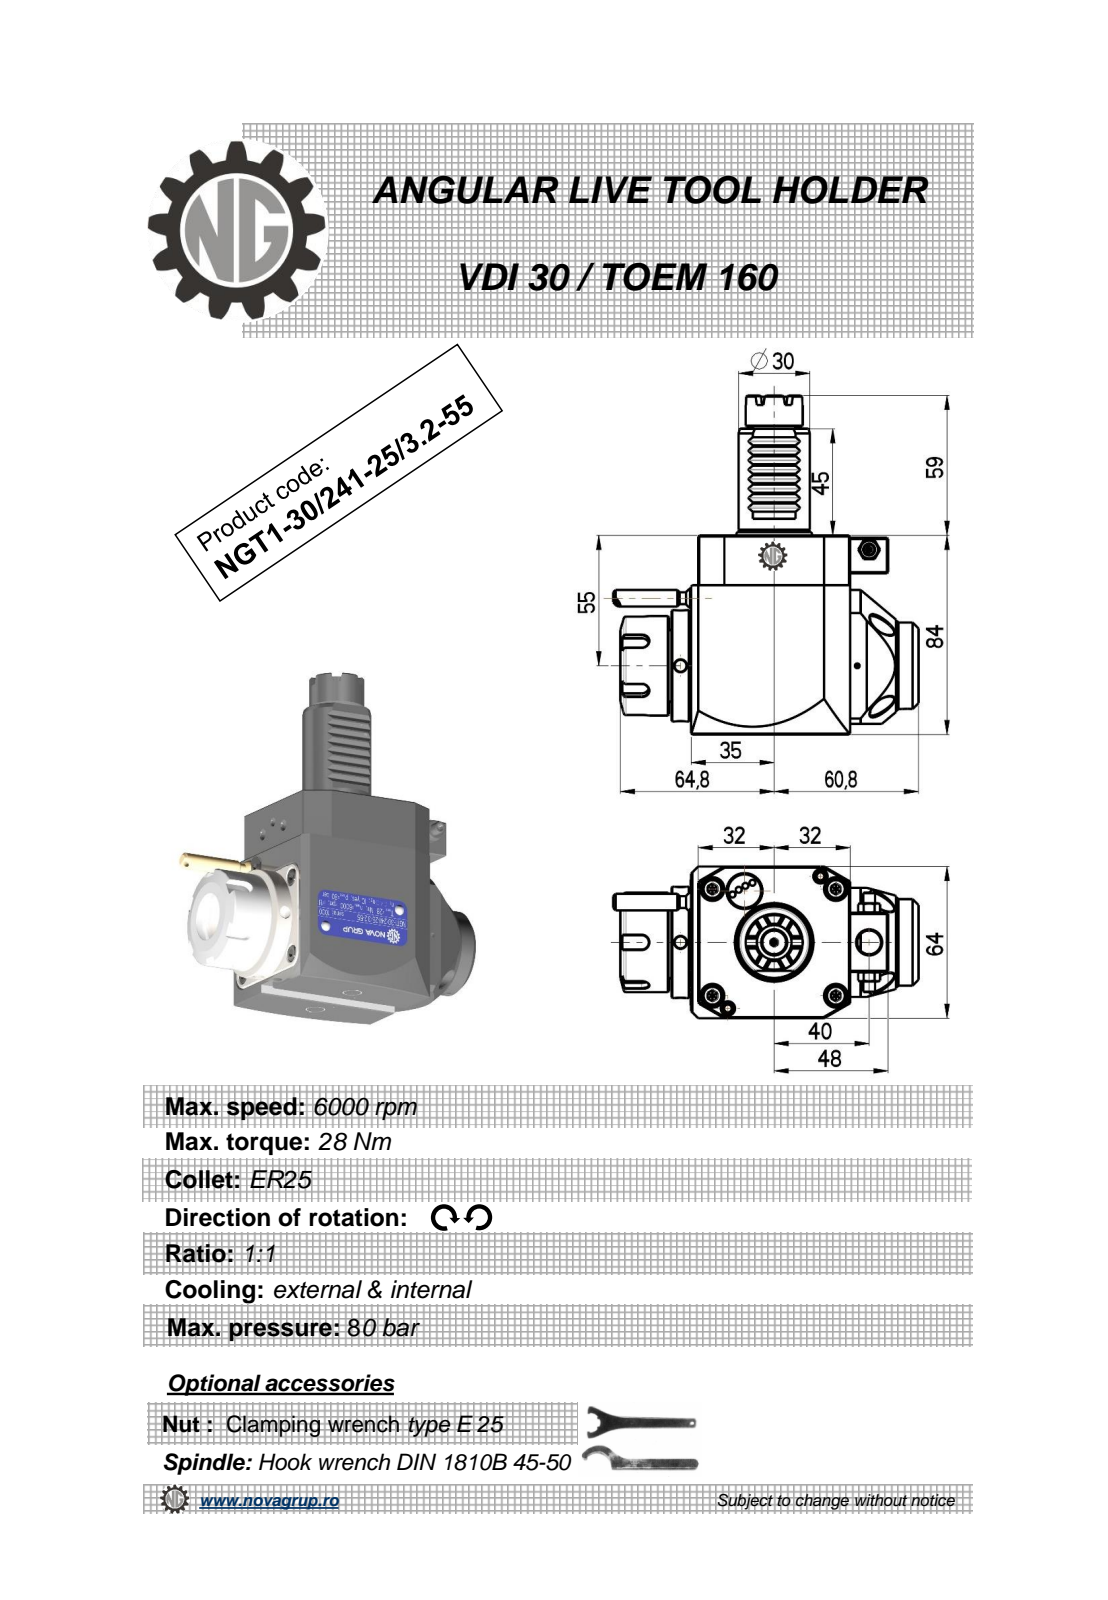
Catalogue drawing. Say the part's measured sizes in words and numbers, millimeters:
The part is named "NGT1_30_241_25_3_2_55". Its 3-D file was written by "PRO/ENGINEER BY PARAMETRIC TECHNOLOGY CORPORATION, 2010280 (CONFIG_CONTROL_DESIGN)". It is 1 solid with 459 faces: 213 planar, 88 cylindrical and 158 other. Overall it measures 143 by 128.63 by 64 millimeters. Its volume is 473 987 cubic millimeters and its surface area 48 697 square millimeters. Round holes: 2 of diameter 5, 1 of diameter 2.5, 1 of diameter 3, 1 of diameter 4.2, 1 of diameter 9.5, 1 of diameter 10, 1 of diameter 20.3. Round bosses or shafts: 2 of diameter 8.96, 2 of diameter 5, 1 of diameter 47, 1 of diameter 42, 1 of diameter 36.5, 1 of diameter 35, 1 of diameter 30, 1 of diameter 24. Partial cylindrical surfaces (rounded edges, fillets, slot ends): 12 of radius 0.26, 8 of radius 0.3, 5 of radius 3, 2 of radius 160, 1 of radius 7.6, 1 of radius 32. The main face-to-face distances are 64, 84, 0.5, 67.2, 67, 80, 3.2, 3, 7.5, 8. The hole center spacings are 24.76, 33.19, 46.5, 79.45, 93.35.
